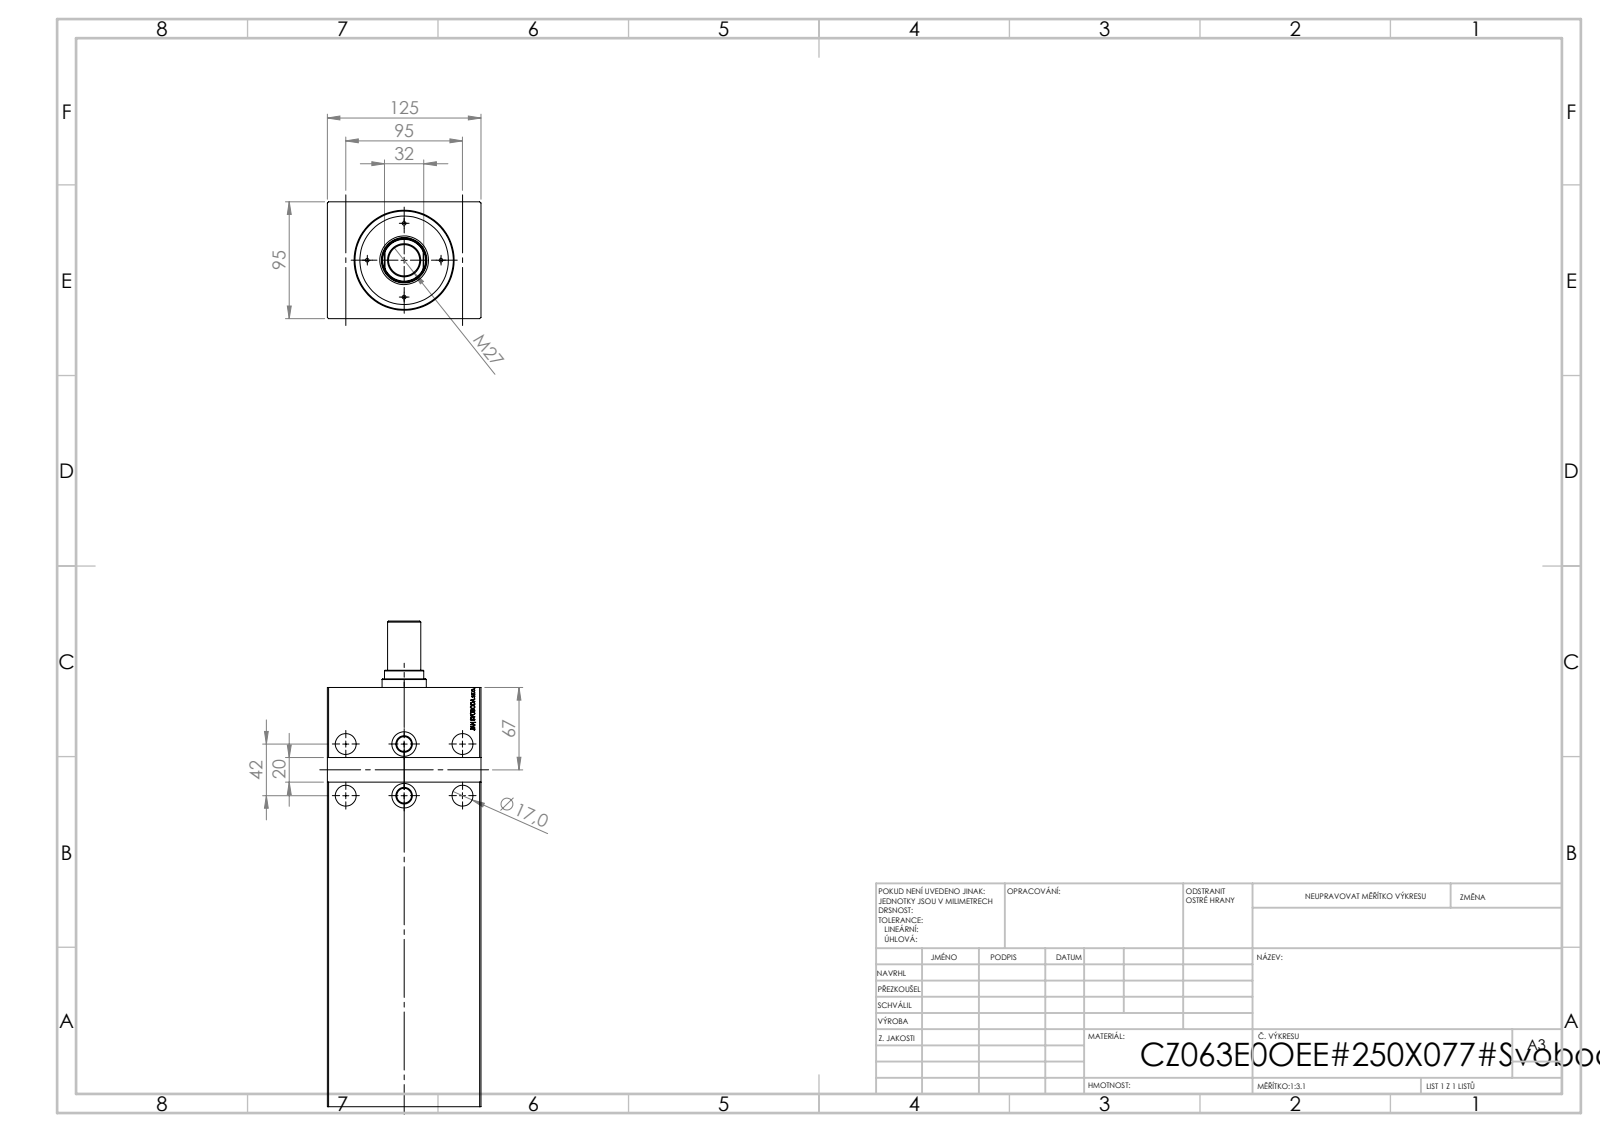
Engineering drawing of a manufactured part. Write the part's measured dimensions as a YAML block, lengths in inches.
step_written_by: "SolidWorks 2019 (CONFIG_CONTROL_DESIGN)"
units: inches
bodies: {solids: 1, faces: 807, planar: 395, cylindrical: 30, other: 382}
overall_size: [13.425, 4.921, 3.74]
volume: 178.9
surface_area: 398
round_holes:
  - {diameter: 0.669, count: 4}
  - {diameter: 0.315, count: 2}
  - {diameter: 0.472, count: 2}
  - {diameter: 0.787, count: 2}
  - {diameter: 1.417, count: 1}
  - {diameter: 2.48, count: 1}
  - {diameter: 3.15, count: 1}
round_bosses_or_shafts:
  - {diameter: 0.531, count: 2}
face_to_face_distances: [3.74, 4.921, 13.425, 12.606, 0.819, 0.079, 3.661, 0.551, 12.055, 12.874]
hole_center_spacings: [1.87, 2.496, 1.654, 3.74, 4.089, 0.841, 1.089, 2.055]
